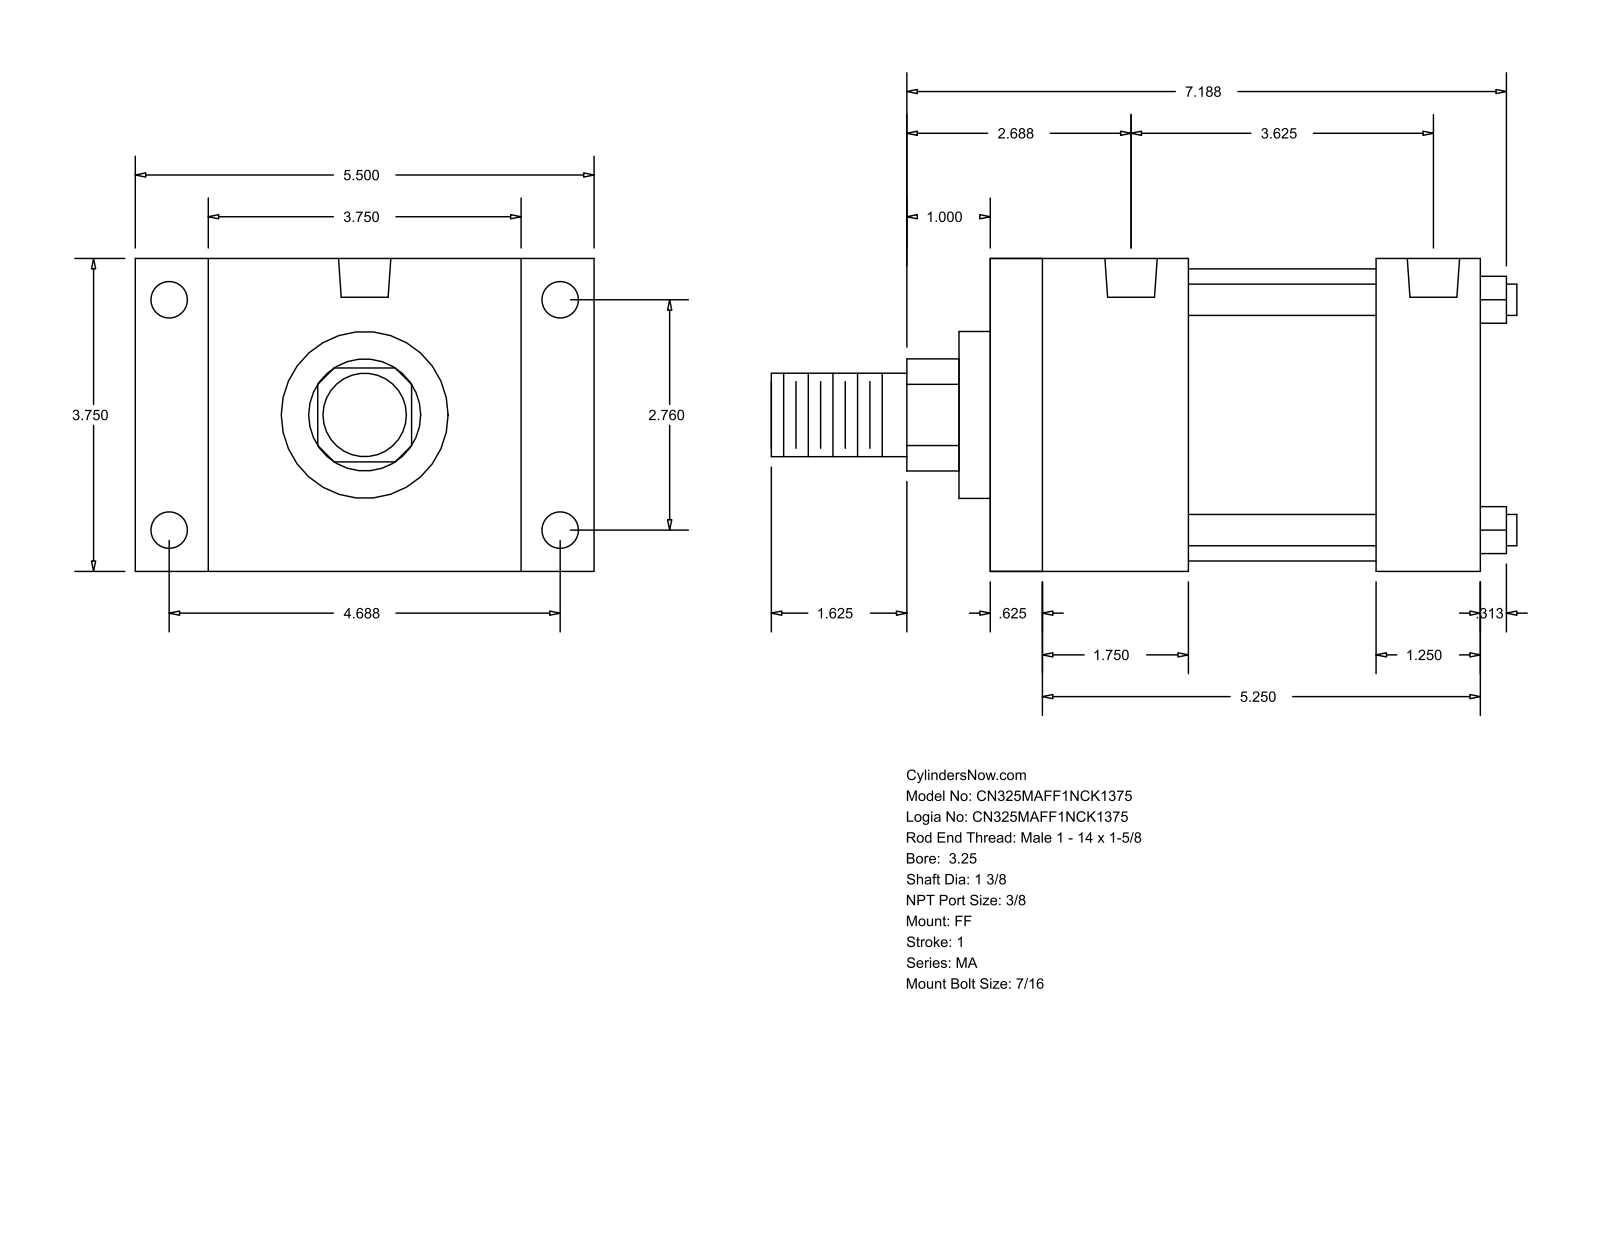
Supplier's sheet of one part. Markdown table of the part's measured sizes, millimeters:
| quantity | value |
| --- | --- |
| part name | MA_FF__0325_1.375 |
| STEP written by | GSSL Pune (CONFIG_CONTROL_DESIGN) |
| units | millimeters |
| bodies | 0 solids, 92 faces (64 planar, 28 cylindrical, 0 other) |
| overall size | 227.01 × 139.7 × 95.25 |
| round holes (diameter × count) | 11.11 × 8, 15.93 × 2 |
| round bosses / shafts (diameter × count) | 9.53 × 4, 88.9 × 1, 50.8 × 1, 34.92 × 1, 25.4 × 1 |
| partial cylindrical surfaces (radius × count) | 17.06 × 1 |
| main face-to-face distances | 95.24, 149.22, 15.87, 133.35, 22.23, 117.47, 60.32, 117.48, 44.45, 101.61 |
| hole center spacings | 4.77, 70.1, 82.54, 87.31, 119.06, 138.16, 92.08 |
